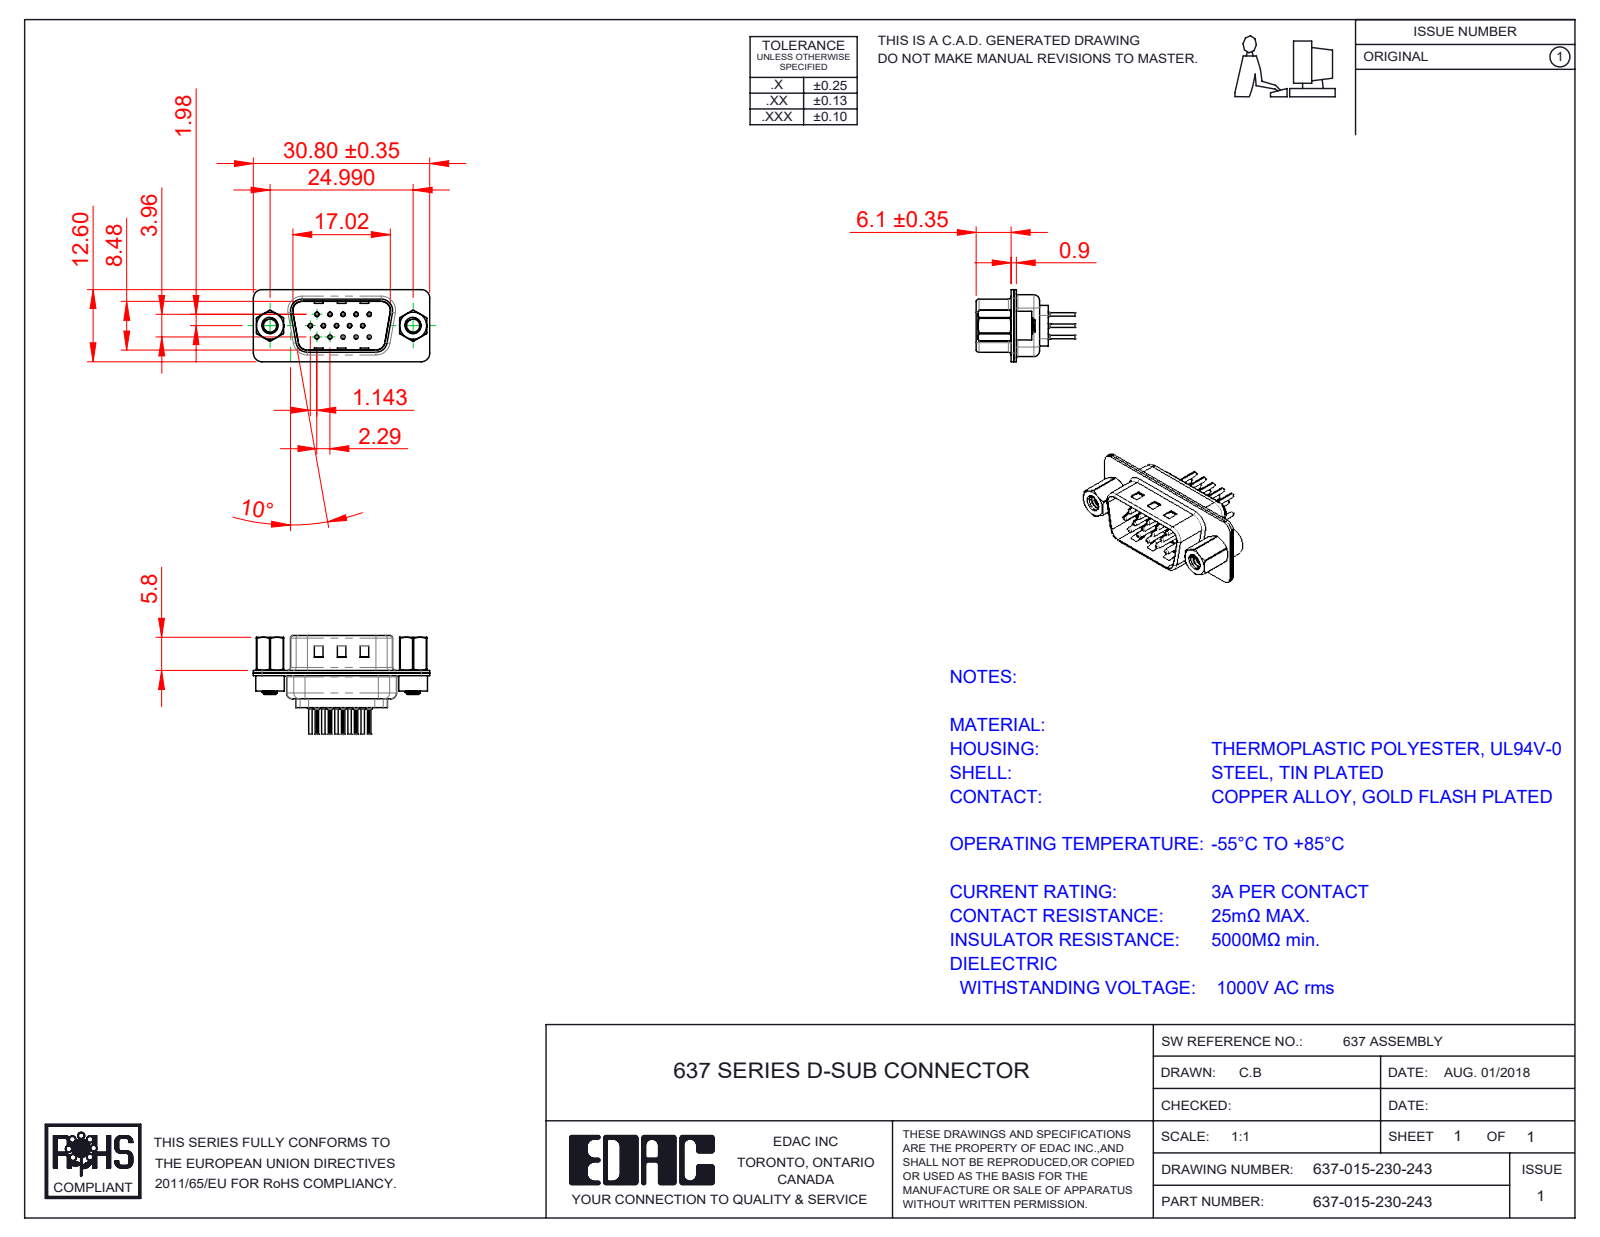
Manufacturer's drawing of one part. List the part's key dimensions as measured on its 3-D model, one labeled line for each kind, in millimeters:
Part name (STEP PRODUCT): 637 4-40 Hex Standoff; 637-015-230-243; 637 Housing_15 Contacts; 637 4-40 Threaded Rivet (+5 more)
STEP written by: SolidWorks 2020 (CONFIG_CONTROL_DESIGN)
Units: millimetres
Bodies: 22 solids, 1930 faces (489 planar, 756 cylindrical, 685 other)
Overall size (bounding box): 30.8 × 17.25 × 12.6
Volume: 1 529 mm³ · Surface area: 5 130 mm²
Round holes (diameter × count): ⌀0.2 ×15, ⌀0.35 ×15, ⌀1.1 ×15, ⌀1.6 ×15, ⌀2.26 ×2, ⌀2.29 ×2, ⌀4 ×2, ⌀4.8 ×2
Round bosses / shafts (diameter × count): ⌀2 ×15, ⌀1.5 ×15, ⌀0.75 ×15, ⌀0.6 ×15, ⌀5 ×2, ⌀4.9 ×2, ⌀2.79 ×2
Partial cylindrical surfaces — rounded edges, fillets, slot ends (radius × count): R0.1 ×30, R1.5 ×16, R2 ×12, R0.5 ×8, R0.25 ×4, R0.55 ×4, R0.7 ×4, R0.95 ×4
Main face-to-face distances: 0.45, 0.9, 0.4, 0.7, 8.88, 8.48, 1.05, 0.31, 4.55, 6.5
Hole centre spacings: 3.96, 2.28, 4.57, 2.29, 6.05, 6.86, 7.92, 6.04
